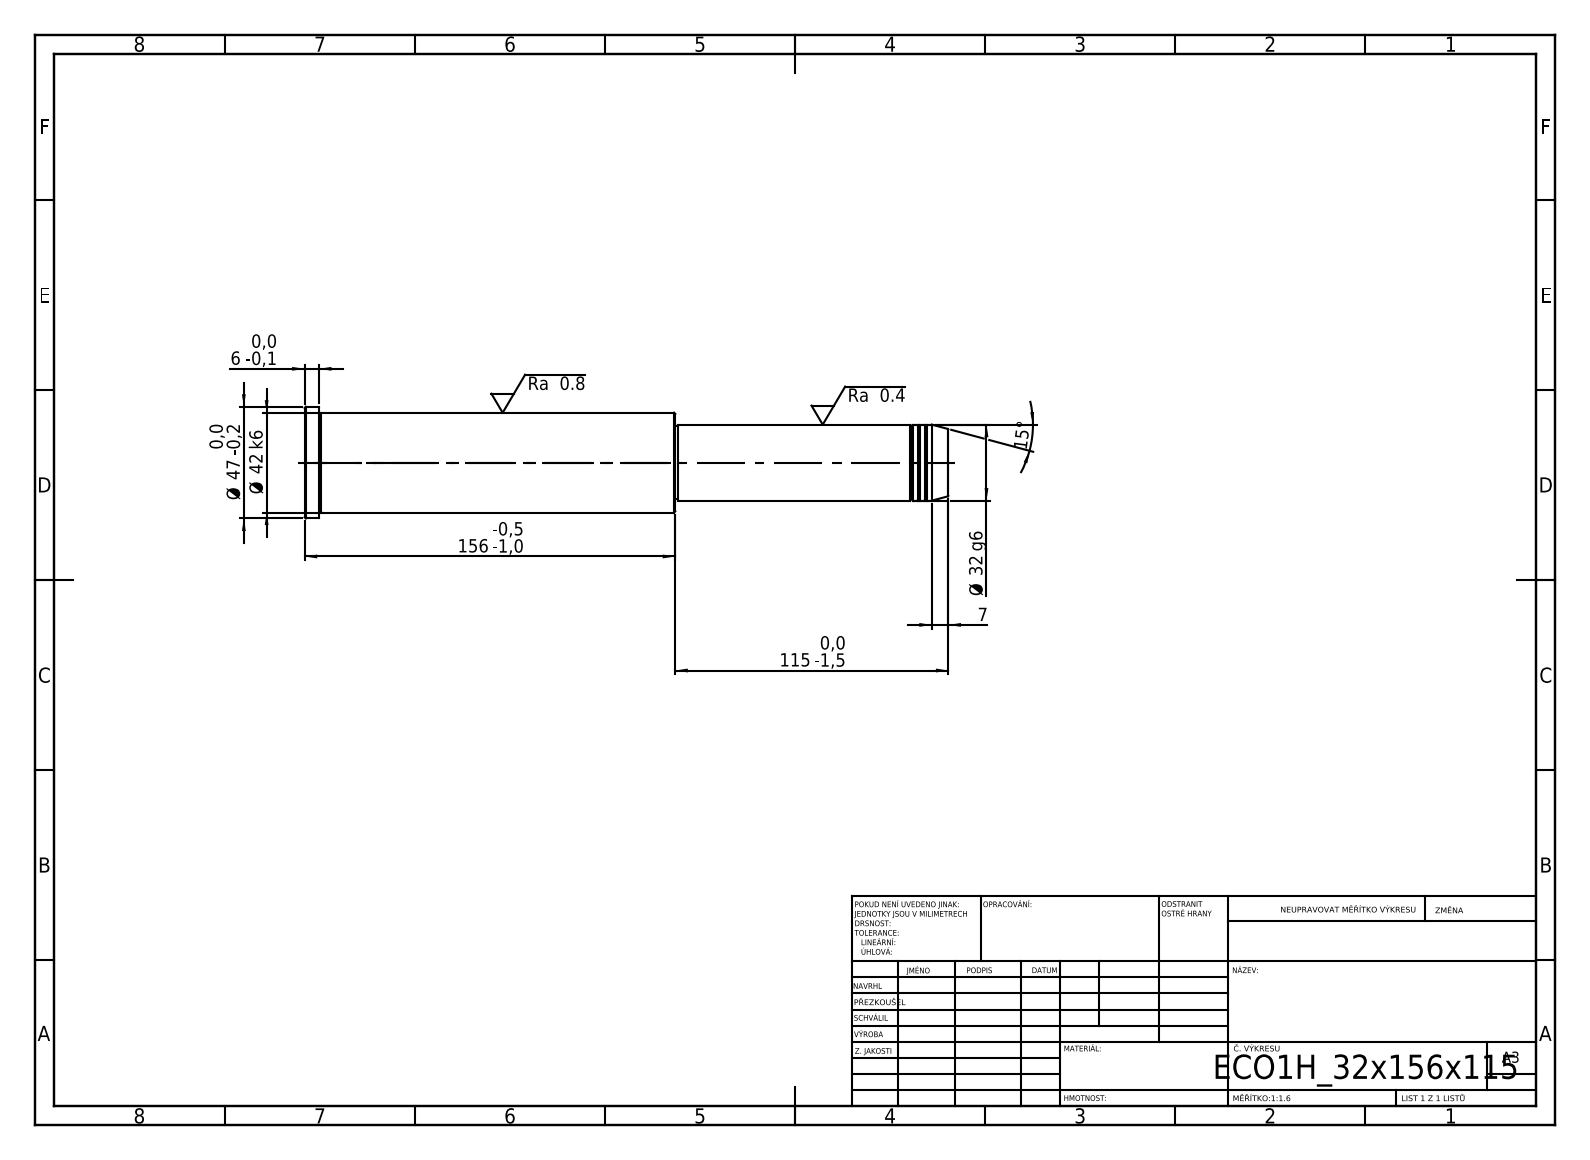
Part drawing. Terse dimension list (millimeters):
written by: SolidWorks 2019 (CONFIG_CONTROL_DESIGN)
unit: mm
bodies: 1 solid, 43 faces (5 planar, 14 cylindrical, 24 other)
size: 271 × 47 × 47
volume: 309 826 mm³; area: 35 752 mm²
bosses: 1× ⌀47, 1× ⌀42, 1× ⌀32, 1× ⌀31
face distances: 271, 115, 156, 265, 150, 6, 114, 1, 151, 157
